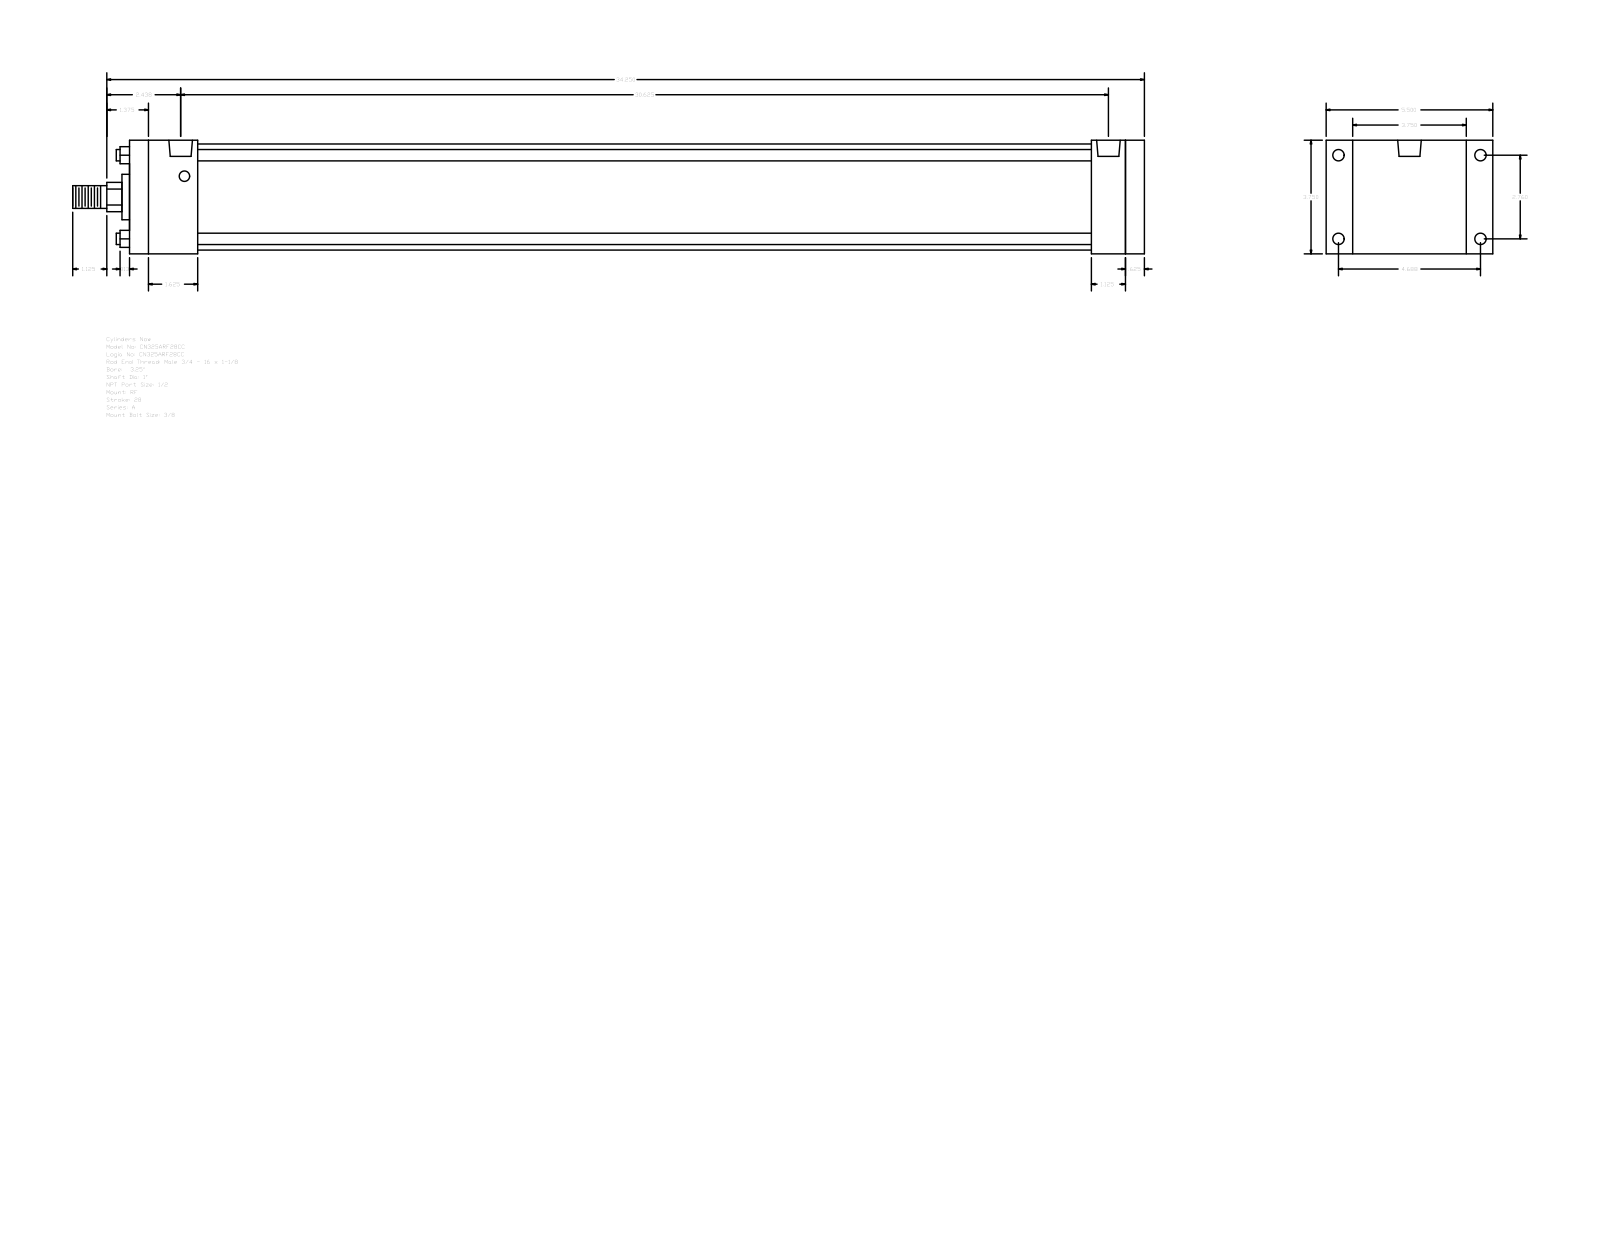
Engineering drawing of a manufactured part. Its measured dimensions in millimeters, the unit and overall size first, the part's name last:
Units: millimetres
Overall size (bounding box): 898.52 × 139.7 × 95.25
Round holes (diameter × count): ⌀8.73 ×4, ⌀9.53 ×4, ⌀19.77 ×2
Round bosses / shafts (diameter × count): ⌀9.53 ×4, ⌀88.9 ×1, ⌀38.1 ×1, ⌀25.4 ×1, ⌀19.05 ×1
Partial cylindrical surfaces — rounded edges, fillets, slot ends (radius × count): R12.29 ×1
Main face-to-face distances: 95.24, 850.9, 835.03, 15.87, 22.23, 117.47, 806.45, 28.58, 44.45, 57.15
Hole centre spacings: 3.18, 70.1, 119.06, 138.16, 771.52, 774.7, 777.88
Bodies: 0 solids, 92 faces (64 planar, 28 cylindrical, 0 other)
Part name (STEP PRODUCT): A_RF__0325_1
STEP written by: GSSL Pune (CONFIG_CONTROL_DESIGN)
